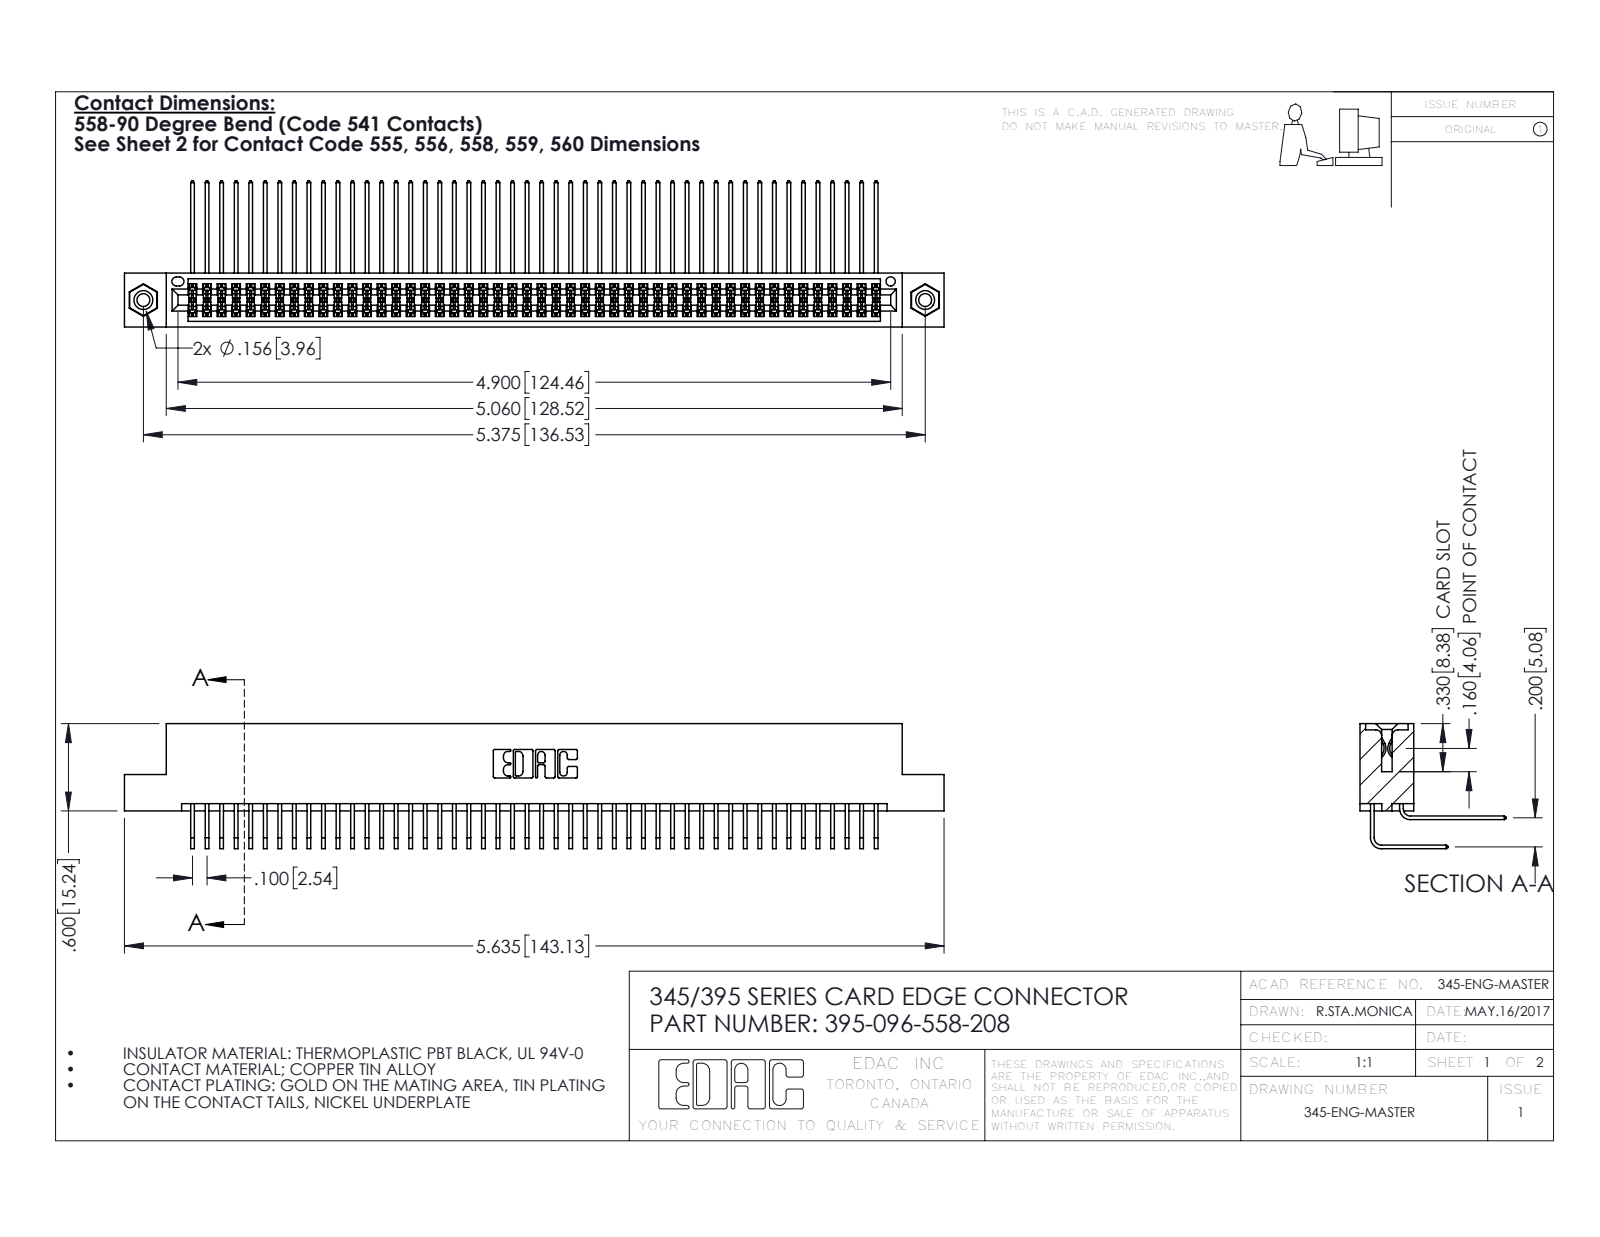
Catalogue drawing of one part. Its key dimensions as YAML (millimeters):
part_name: "395-096-558-208; 345-292-001_558 Tail - 2; 345-250-001_345-250-003-102; 345 Part_Flush Mounting Lugs - 0.156 Dia-TI (+1 more)"
step_written_by: "SolidWorks 2016 (CONFIG_CONTROL_DESIGN)"
units: millimeters
bodies: {solids: 99, faces: 5178, planar: 3472, cylindrical: 1690, other: 16}
overall_size: [143.1, 25.5, 21.8]
volume: 14500
surface_area: 24170
round_holes:
  - {diameter: 2.3, count: 2}
  - {diameter: 3.2, count: 2}
  - {diameter: 4, count: 2}
  - {diameter: 1.6, count: 1}
round_bosses_or_shafts:
  - {diameter: 3.9, count: 2}
partial_cylinders:
  - {radius: 0.2, count: 145}
  - {radius: 0.3, count: 22}
  - {radius: 0.2, count: 6}
  - {radius: 0.8, count: 6}
  - {radius: 0.7, count: 3}
  - {radius: 0.4, count: 2}
  - {radius: 0.5, count: 2}
  - {radius: 0.6, count: 2}
face_to_face_distances: [1.8, 7.6, 5.1, 9.4, 2.5, 6.9, 0.6, 5.7, 0.6, 4.4]
hole_center_spacings: [6.9, 130.5, 136.5]
